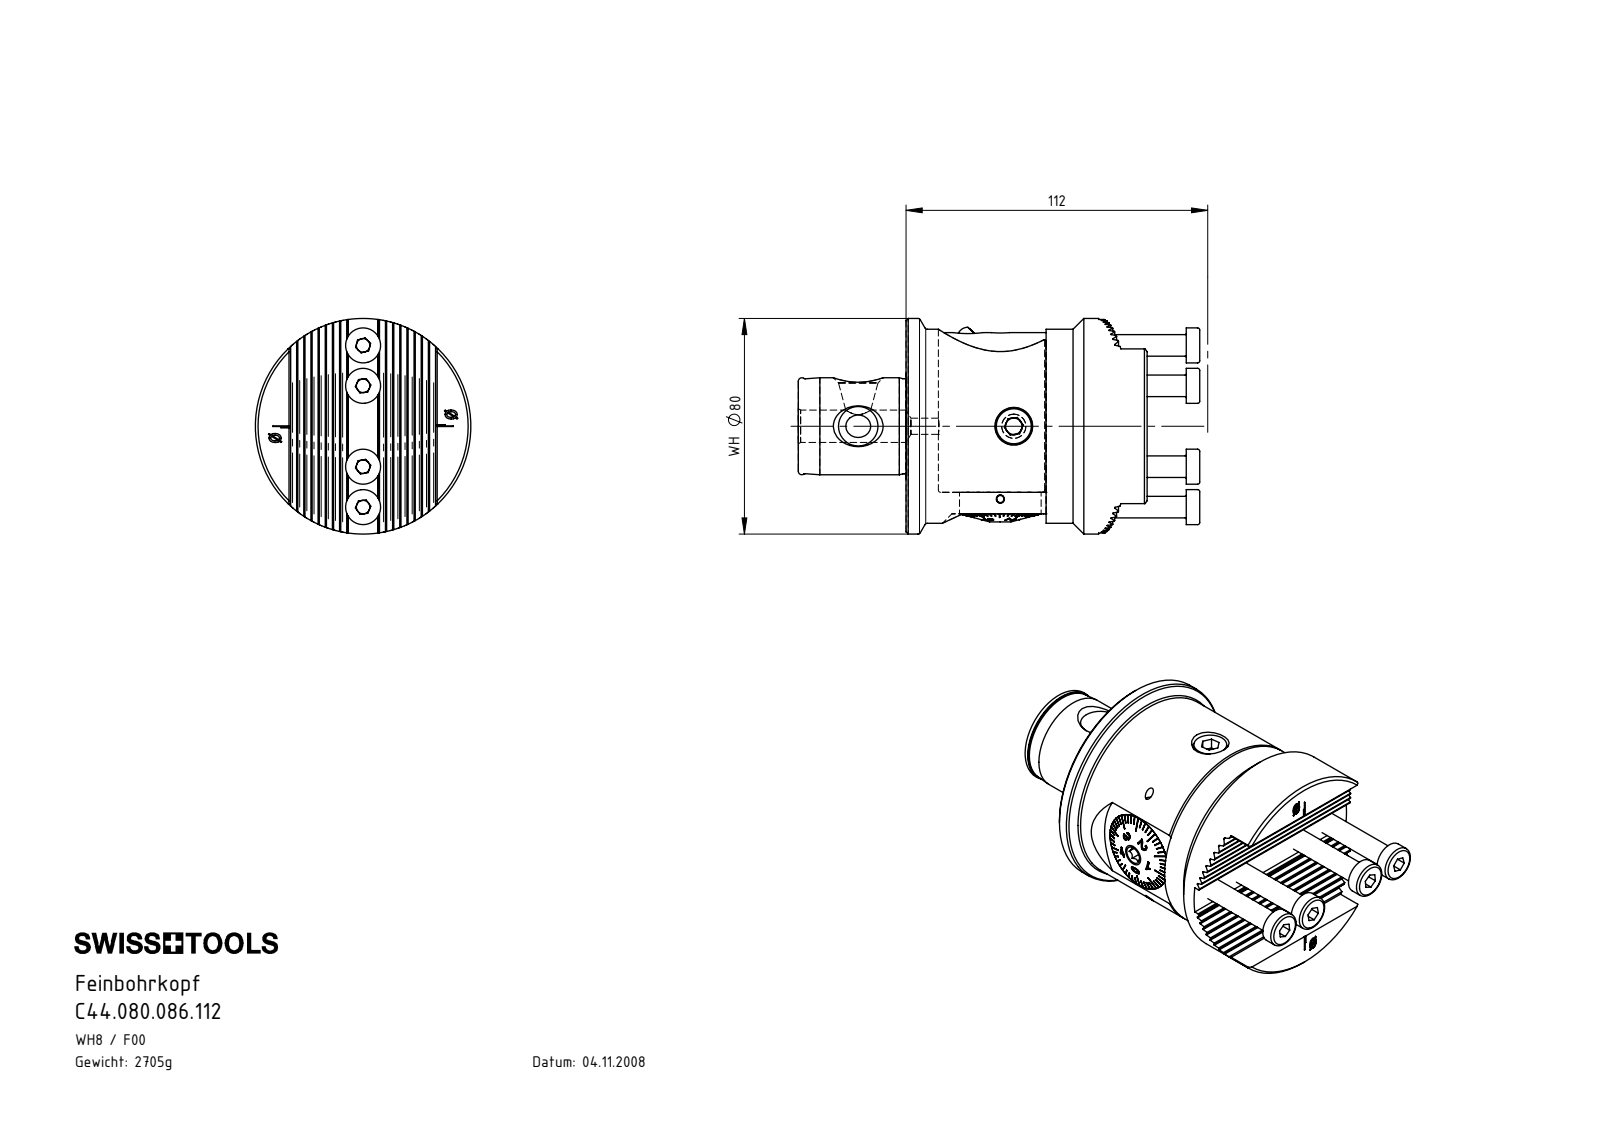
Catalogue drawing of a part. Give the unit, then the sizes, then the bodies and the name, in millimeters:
Units: millimetres
Overall size (bounding box): 149.03 × 80 × 80
Round holes (diameter × count): ⌀5 ×5, ⌀6.8 ×4, ⌀7 ×4, ⌀10 ×4, ⌀10.5 ×4, ⌀3 ×2, ⌀6 ×2, ⌀1 ×1, ⌀3.15 ×1, ⌀3.3 ×1, ⌀6.5 ×1, ⌀7.75 ×1
Round bosses / shafts (diameter × count): ⌀8 ×6, ⌀13 ×5, ⌀10 ×4, ⌀6 ×4, ⌀80 ×1, ⌀72 ×1, ⌀36 ×1, ⌀35.3 ×1
Partial cylindrical surfaces — rounded edges, fillets, slot ends (radius × count): R0.2 ×16, R10.25 ×1, R23 ×1, R36 ×1
Main face-to-face distances: 52, 2.38, 4.76, 7.14, 7.15, 9.53, 4.77, 11.91, 14.29, 9.52
Hole centre spacings: 12, 12.04, 15, 18.44, 20, 33.24, 34.18, 47.54
Volume: 360 769 mm³ · Surface area: 92 923 mm²
Bodies: 23 solids, 809 faces (470 planar, 106 cylindrical, 233 other)
Part name (STEP PRODUCT): F00-ER1.101.045_A_PreviewCfg; A55-BG2.001.000_B; F00-BG6.001.008_A; F00-BG5.001.037_B (+8 more)
STEP written by: SolidWorks 2017 (AUTOMOTIVE_DESIGN)
